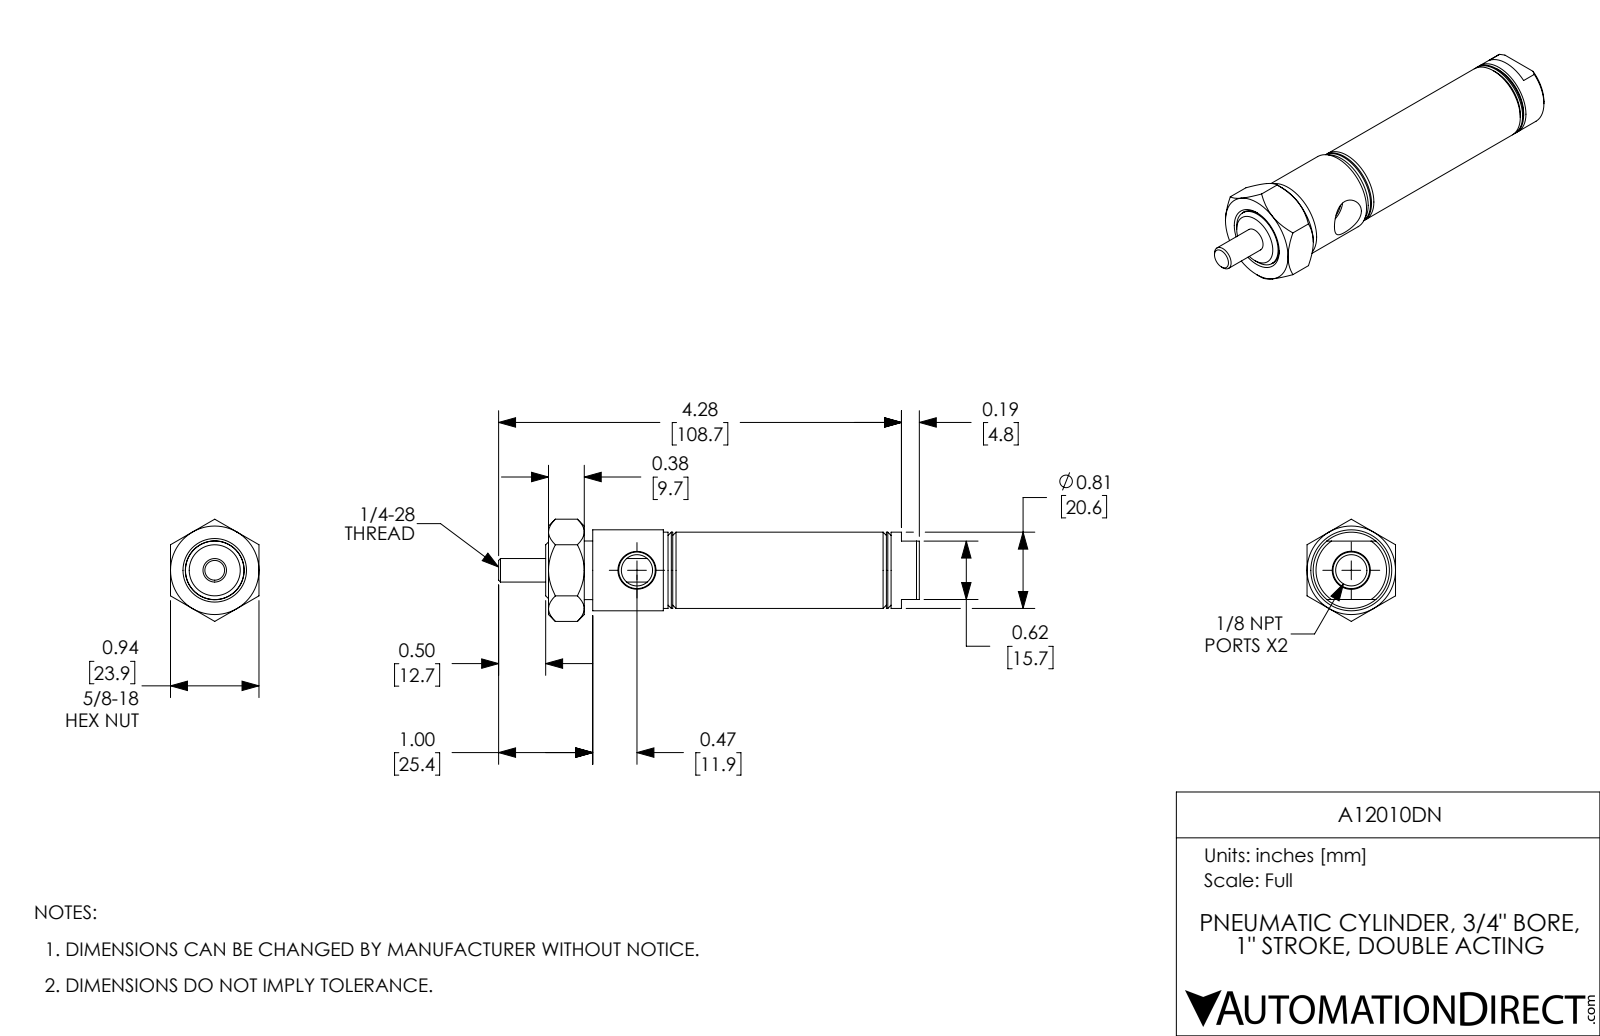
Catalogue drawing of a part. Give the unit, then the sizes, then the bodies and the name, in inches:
Units: inches
Overall size (bounding box): 4.47 × 1.085 × 0.94
Round holes (diameter × count): ⌀0.332 ×2, ⌀0.25 ×1, ⌀0.625 ×1, ⌀0.75 ×1
Round bosses / shafts (diameter × count): ⌀0.86 ×1, ⌀0.81 ×1, ⌀0.623 ×1
Main face-to-face distances: 2.485, 0.94, 0.5, 0.985, 1.485, 1, 1.5, 2.575, 2.075, 1.075
Volume: 1.636 in³ · Surface area: 25.21 in²
Bodies: 3 solids, 94 faces (27 planar, 28 cylindrical, 39 other)
Part name (STEP PRODUCT): A12010DN; A12010DN_Mounting Nut_D-9; A12010DN-Rod; A12010DN-MainBody
STEP written by: SolidWorks 2017 (AUTOMOTIVE_DESIGN)
